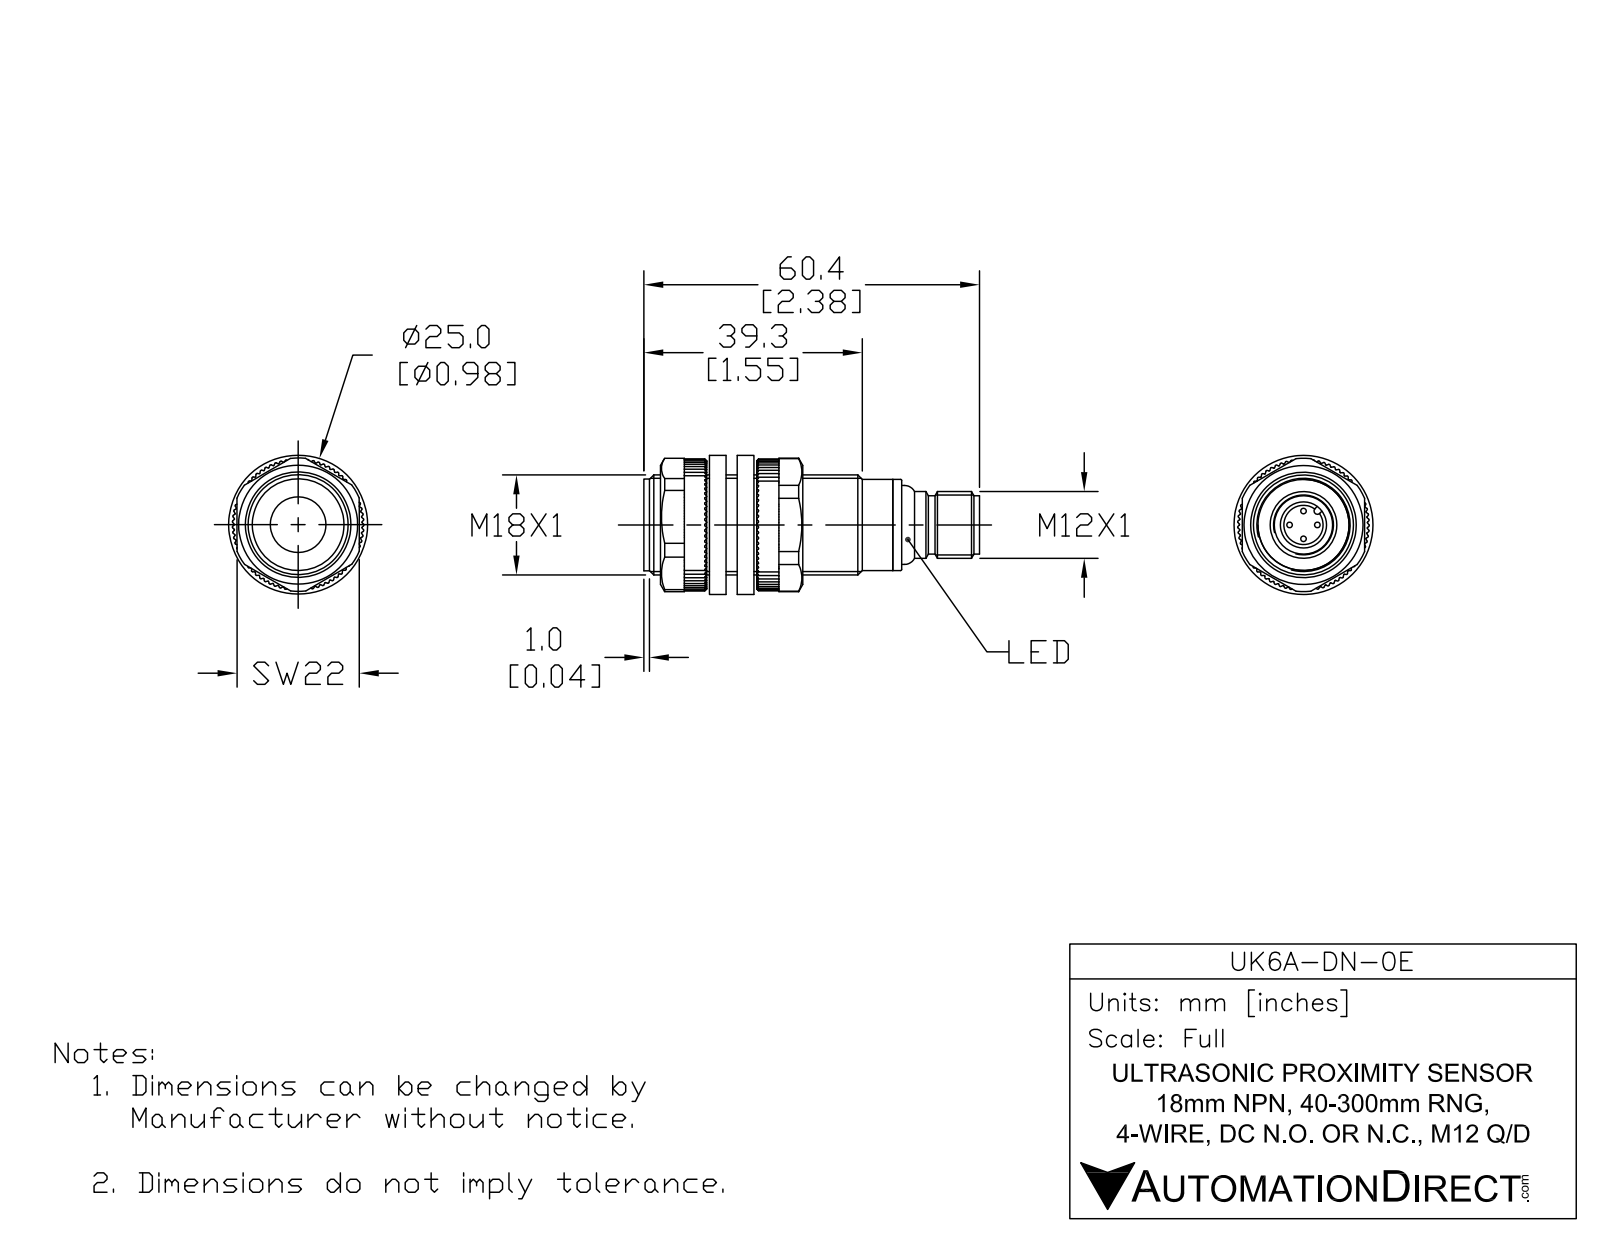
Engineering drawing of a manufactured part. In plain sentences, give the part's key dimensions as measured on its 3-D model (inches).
The part is named "UK6A-DN-0E". Its 3-D file was written by "SolidWorks 2017 (AUTOMOTIVE_DESIGN)". It is 4 solids with 86 faces: 15 planar, 36 cylindrical and 35 other. Overall it measures 2.374 by 0.709 by 0.709 inches. Its volume is 0.759 cubic inches and its surface area 7.648 square inches. Round holes: 1 of diameter 0.276, 1 of diameter 0.327, 1 of diameter 0.374. Round bosses or shafts: 4 of diameter 0.039, 1 of diameter 0.709, 1 of diameter 0.646, 1 of diameter 0.622, 1 of diameter 0.559, 1 of diameter 0.472, 1 of diameter 0.413. Partial cylindrical surfaces (rounded edges, fillets, slot ends): 1 of radius 0.024. The main face-to-face distances are 1.724, 0.039, 1.764, 0.039, 1.763, 1.823, 1.822, 1.783, 0.059, 2.024.
